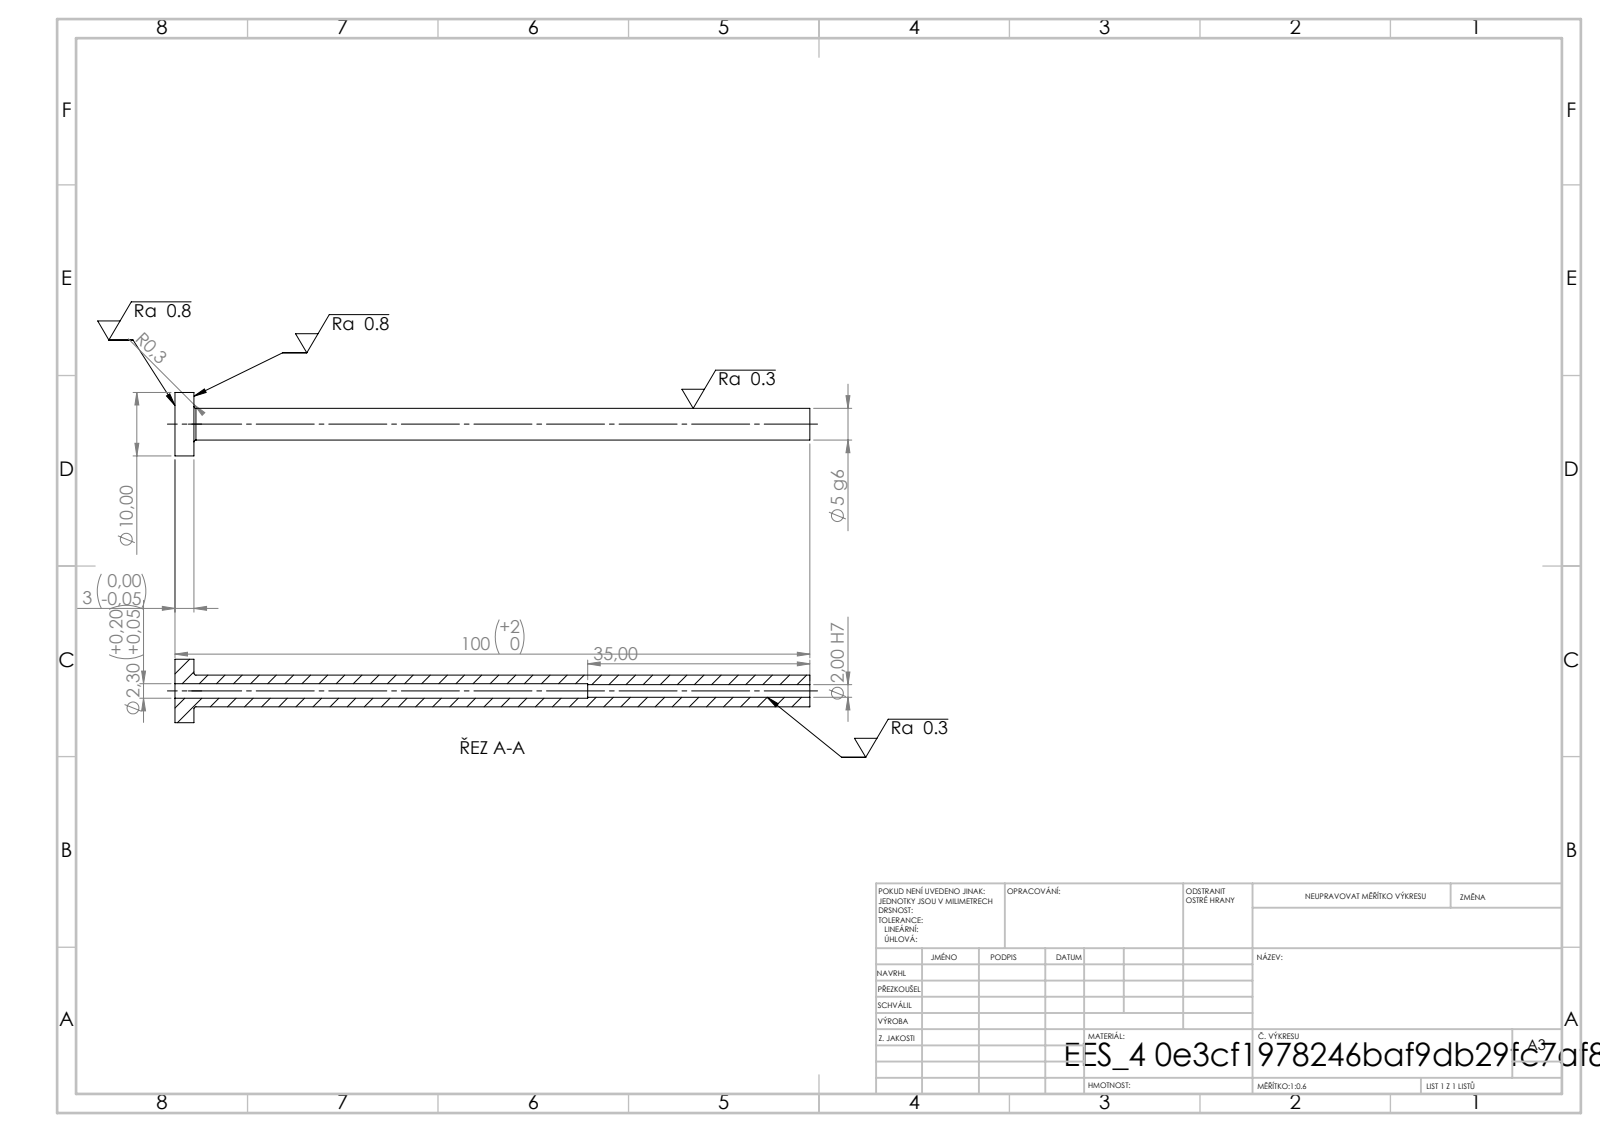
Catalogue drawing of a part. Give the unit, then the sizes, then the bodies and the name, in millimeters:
Units: millimetres
Overall size (bounding box): 100 × 10 × 10
Round holes (diameter × count): ⌀2 ×1, ⌀2.3 ×1
Round bosses / shafts (diameter × count): ⌀10 ×1, ⌀5 ×1
Main face-to-face distances: 3, 100, 97, 65, 62, 35
Volume: 1 761 mm³ · Surface area: 2 456 mm²
Bodies: 1 solid, 14 faces (4 planar, 8 cylindrical, 2 other)
STEP written by: SolidWorks 2019 (CONFIG_CONTROL_DESIGN)
